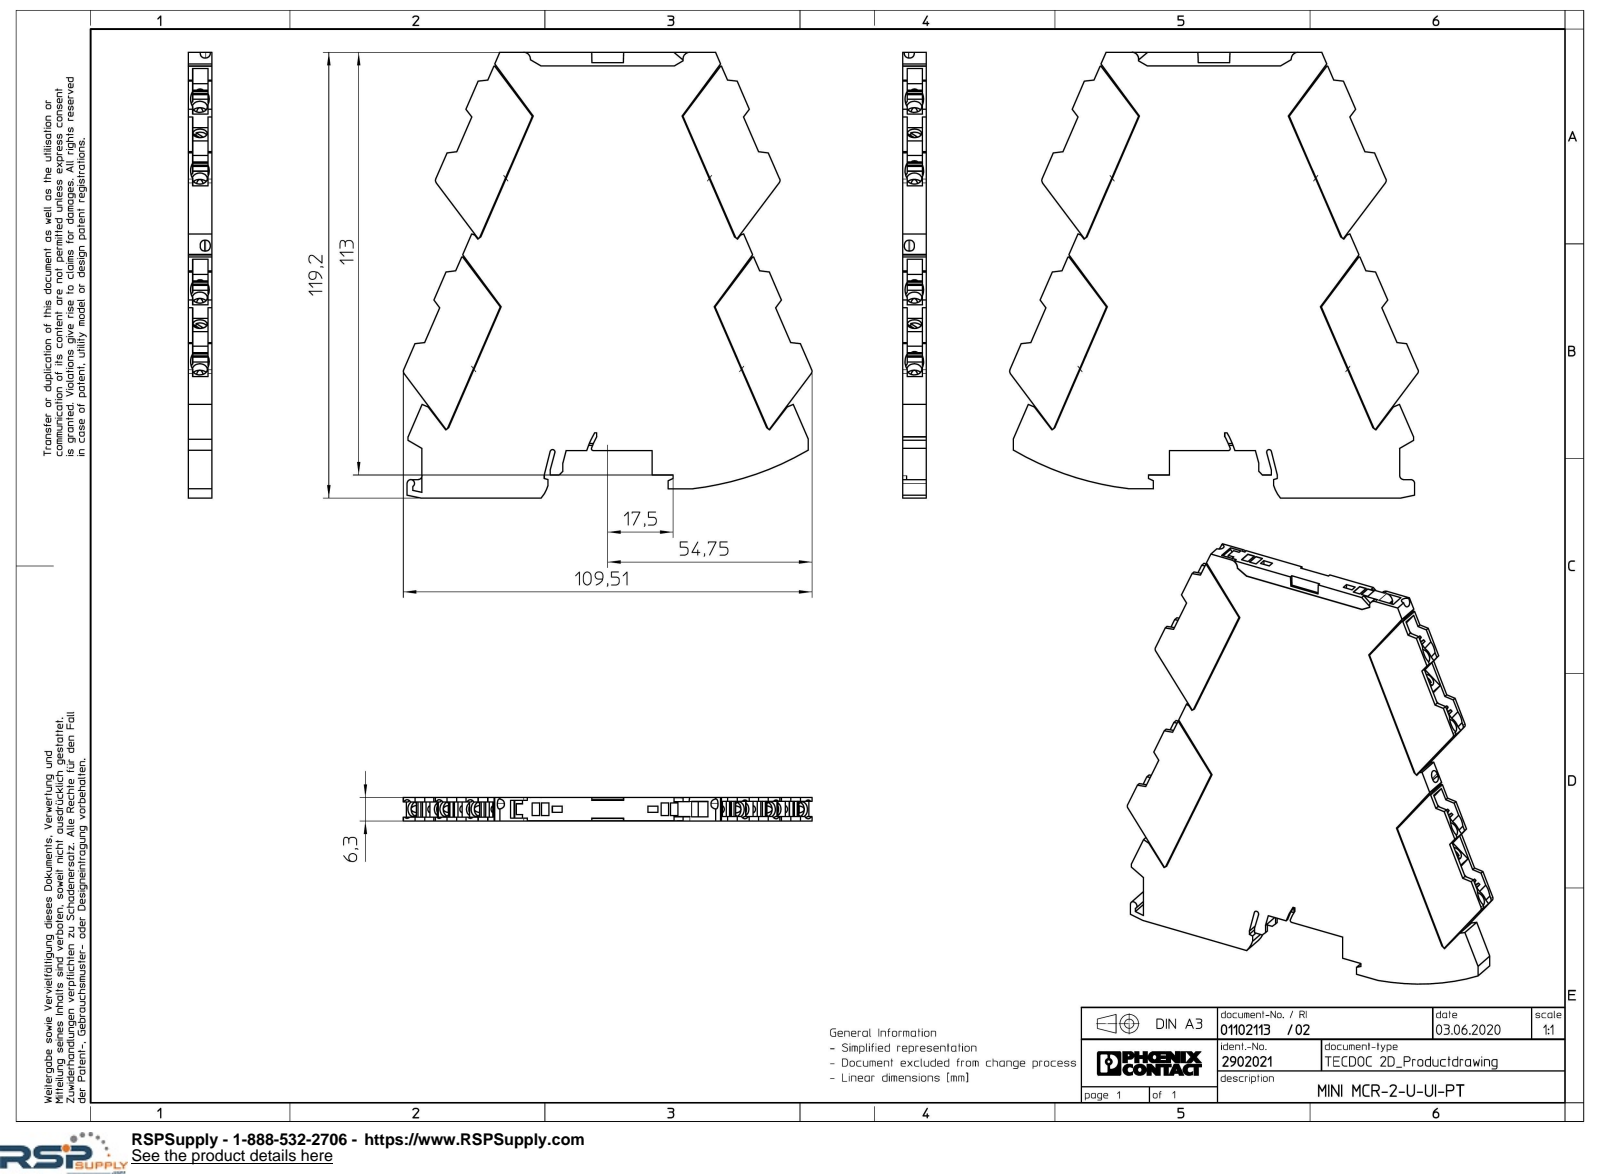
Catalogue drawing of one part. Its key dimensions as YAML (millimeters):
part_name: "MINI_ANALOG_PRO-SOCKEL-select; FASTCON_PRO-SET-PT-select.3; MINI_ANALOG_PRO-PT-select"
step_written_by: "Creo Elements/Direct Modeling 20.1A 29-Sep-2018 (C) Parametric Technology GmbH (AUTOMOTIVE_DESIGN)"
units: millimeters
bodies: {solids: 5, faces: 1234, planar: 1080, cylindrical: 125, other: 29}
overall_size: [119.2, 109.51, 6.3]
volume: 58791
surface_area: 35575
round_holes:
  - {diameter: 2, count: 8}
  - {diameter: 4, count: 8}
  - {diameter: 3.3, count: 4}
  - {diameter: 3.8, count: 4}
round_bosses_or_shafts:
  - {diameter: 3, count: 4}
partial_cylinders:
  - {radius: 3.5, count: 16}
  - {radius: 1.5, count: 8}
  - {radius: 1, count: 6}
  - {radius: 0.2, count: 5}
  - {radius: 1.15, count: 4}
  - {radius: 1.18, count: 4}
  - {radius: 1.8, count: 3}
  - {radius: 0.5, count: 1}
face_to_face_distances: [6.3, 2.65, 5.35, 2.55, 37.57, 2.75, 1.65, 4.72, 0.32, 0.31]
hole_center_spacings: [37.56, 18.2, 6.3, 11.45, 13.05, 5.15, 6.75, 11.9]
